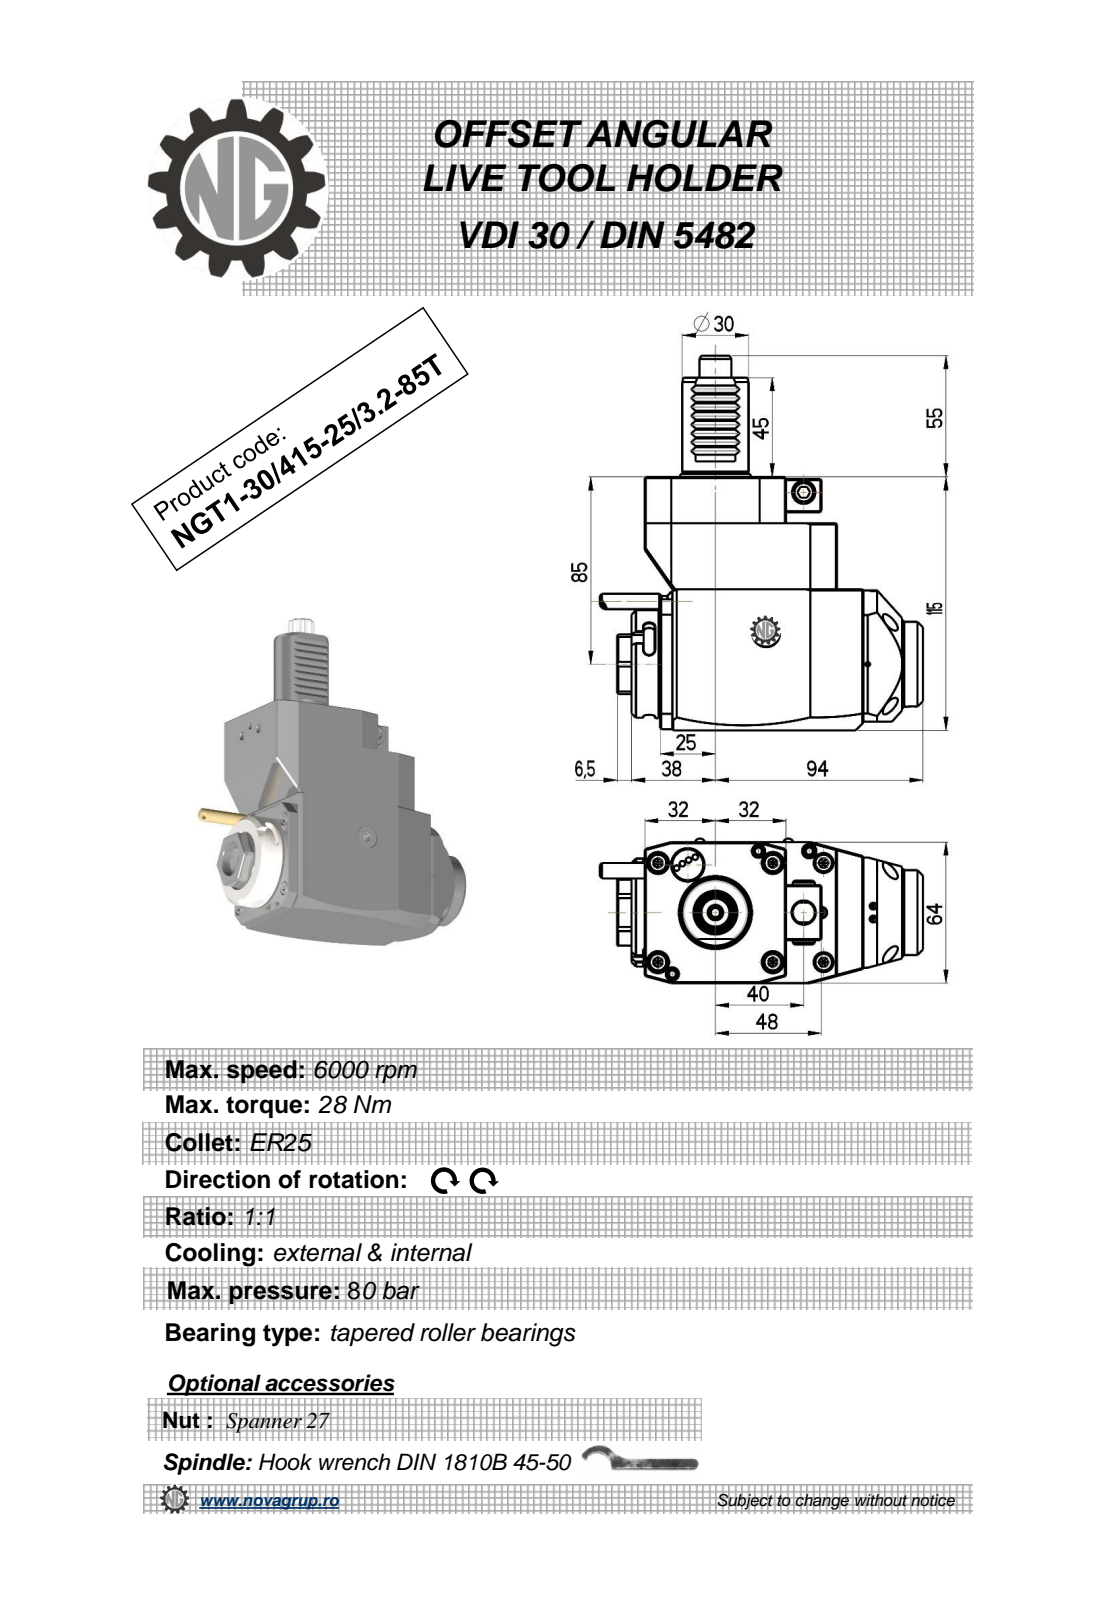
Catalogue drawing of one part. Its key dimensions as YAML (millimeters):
part_name: "NGT1_30_415_25_3_2_85T"
step_written_by: "PRO/ENGINEER BY PARAMETRIC TECHNOLOGY CORPORATION, 2010280 (CONFIG_CONTROL_DESIGN)"
units: millimeters
bodies: {solids: 1, faces: 370, planar: 180, cylindrical: 102, other: 88}
overall_size: [170, 146.38, 64]
volume: 716297
surface_area: 59531
round_holes:
  - {diameter: 2.5, count: 1}
  - {diameter: 3, count: 1}
  - {diameter: 4.2, count: 1}
  - {diameter: 5.3, count: 1}
  - {diameter: 8.5, count: 1}
  - {diameter: 9.5, count: 1}
  - {diameter: 10, count: 1}
  - {diameter: 18, count: 1}
round_bosses_or_shafts:
  - {diameter: 8.96, count: 2}
  - {diameter: 49, count: 1}
  - {diameter: 42, count: 1}
  - {diameter: 38.5, count: 1}
  - {diameter: 30, count: 1}
  - {diameter: 10, count: 1}
  - {diameter: 7, count: 1}
  - {diameter: 5, count: 1}
partial_cylinders:
  - {radius: 2.91, count: 16}
  - {radius: 0.3, count: 8}
  - {radius: 2.5, count: 6}
  - {radius: 180, count: 2}
  - {radius: 4.5, count: 1}
  - {radius: 5.75, count: 1}
  - {radius: 7.25, count: 1}
  - {radius: 15, count: 1}
face_to_face_distances: [64, 115, 7, 80, 87, 6, 94, 21, 12.5, 13]
hole_center_spacings: [34.25, 40, 51.62, 76.5]
